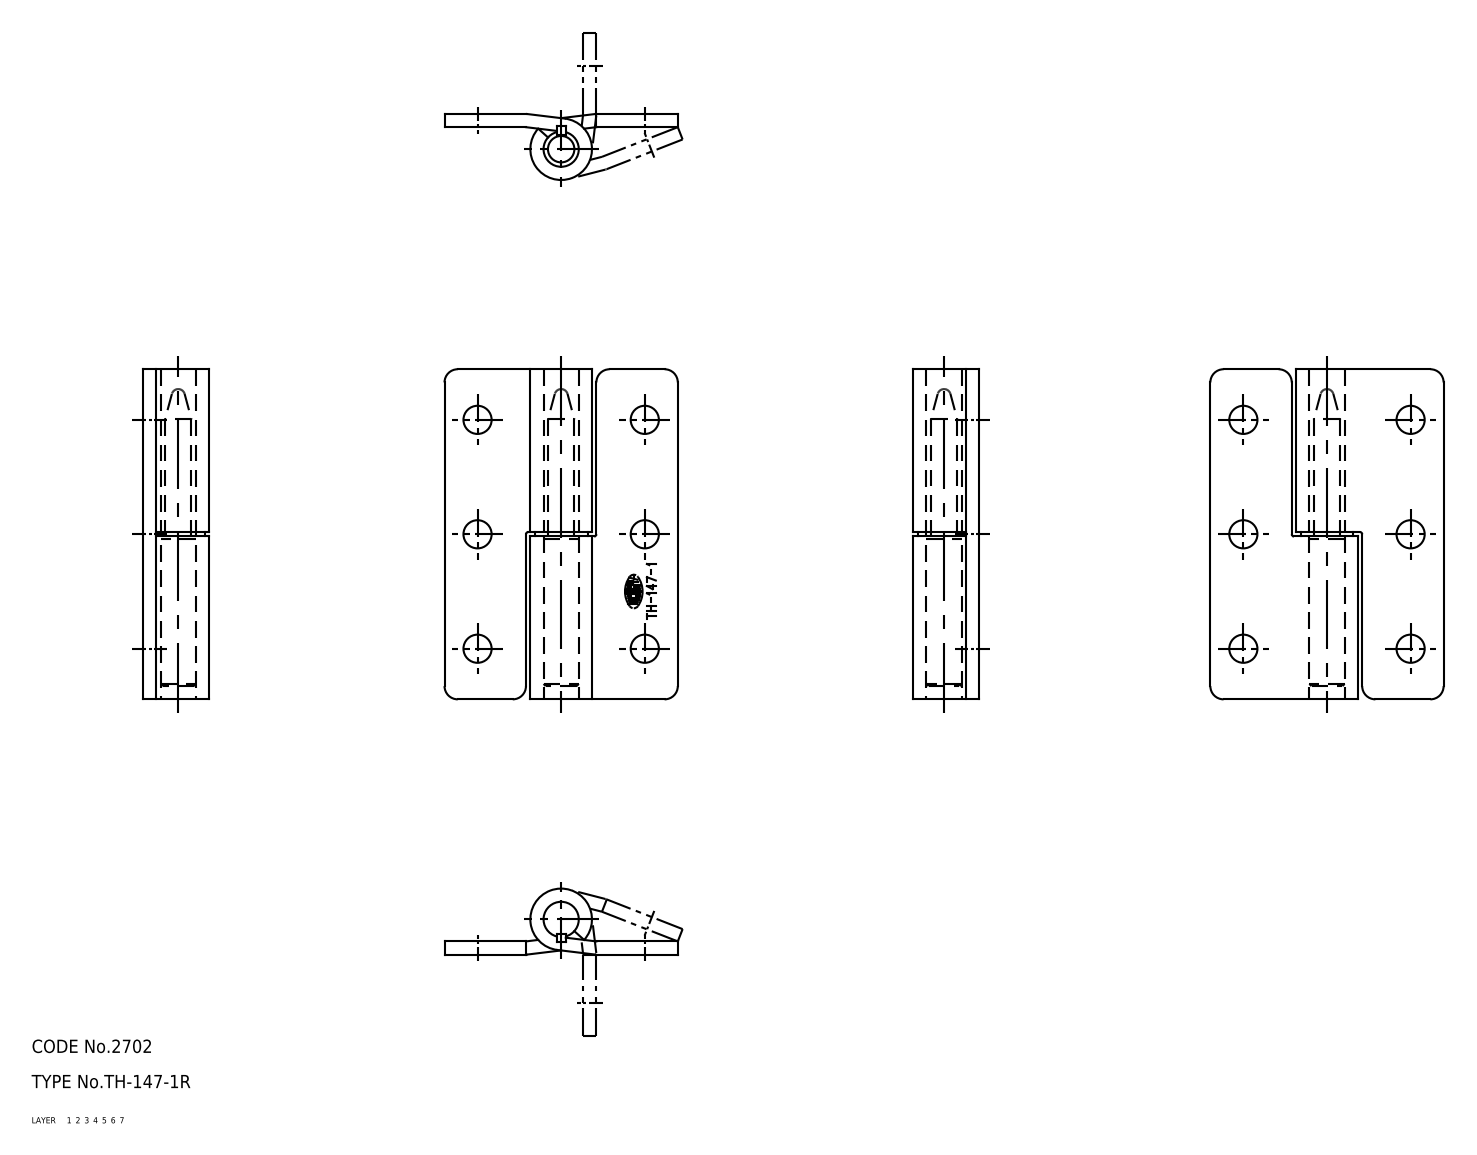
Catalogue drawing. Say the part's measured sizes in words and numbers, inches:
The part is named "67112885; 67112898; 67112911; 67112924". Its 3-D file was written by "CADfix (AUTOMOTIVE_DESIGN)". It is 4 solids with 71 faces: 0 planar, 0 cylindrical and 71 other. Overall it measures 2.953 by 2.087 by 0.591 inches. Its volume is 1.145 cubic inches and its surface area 22.33 square inches.
